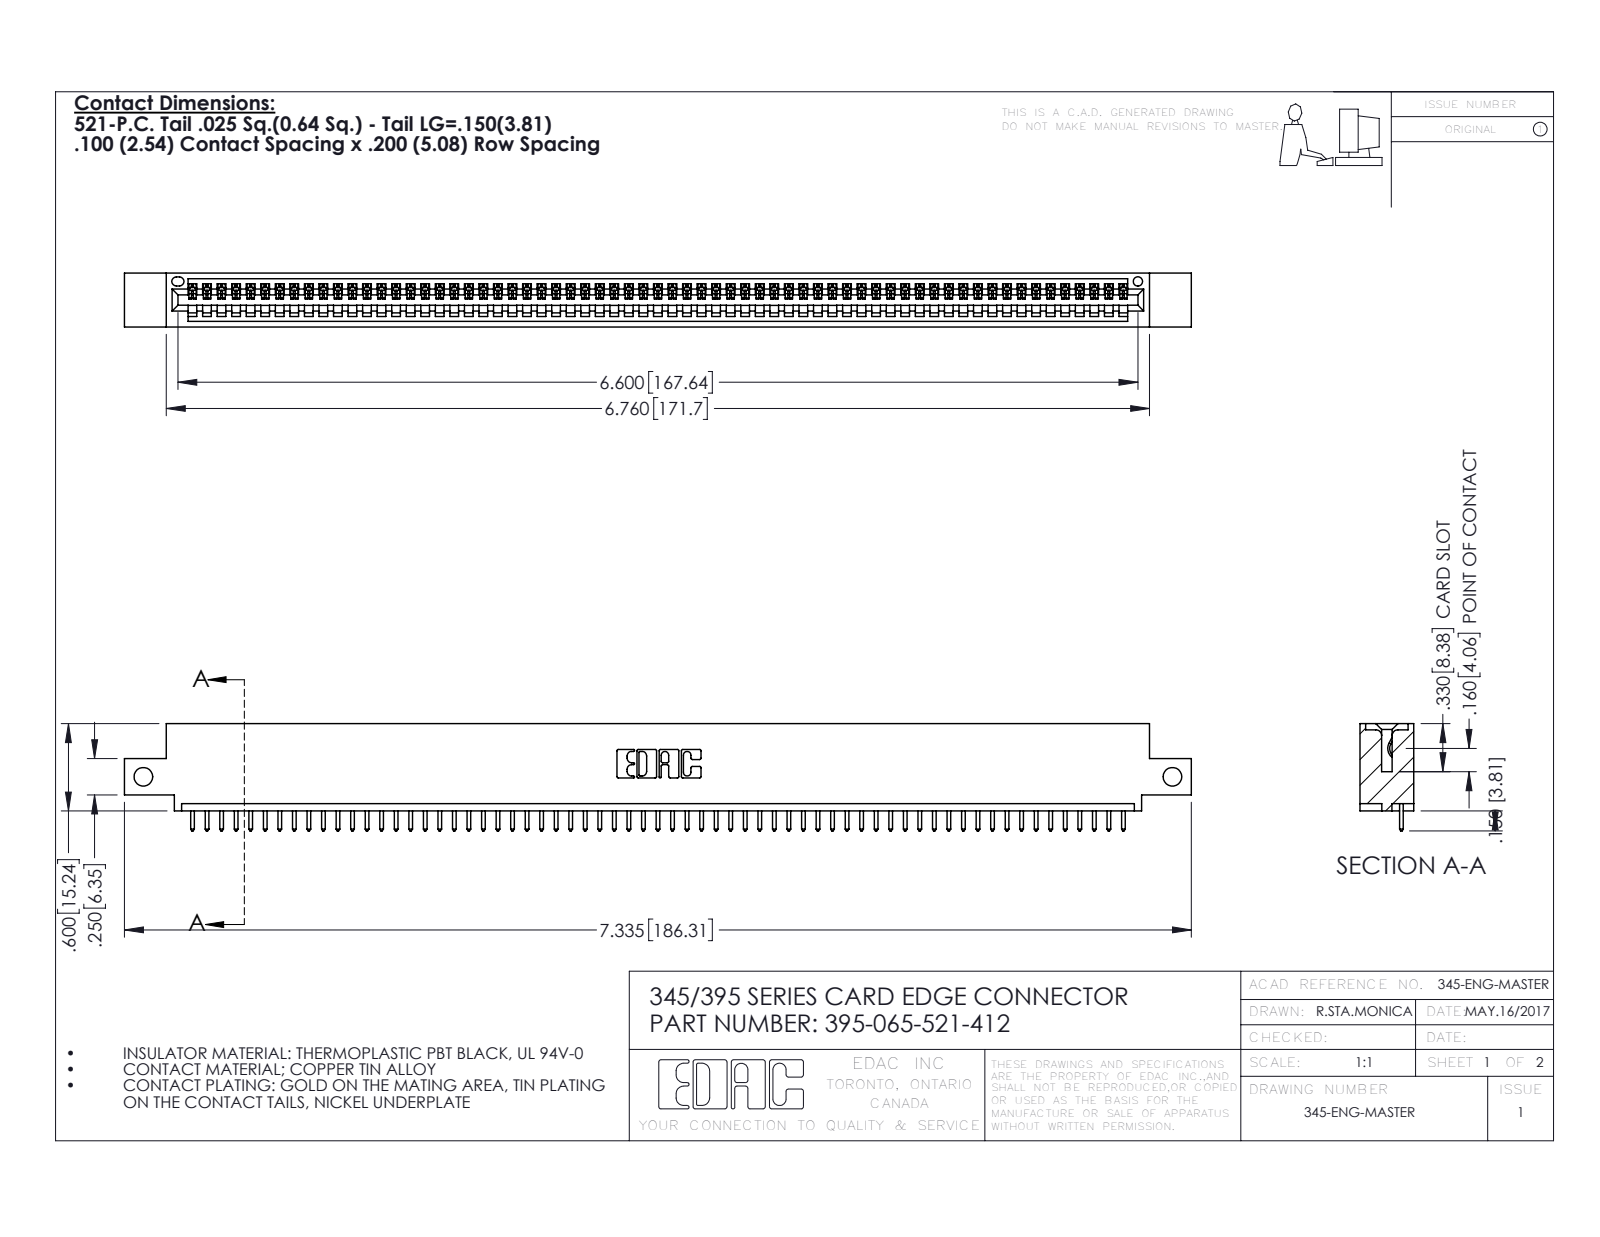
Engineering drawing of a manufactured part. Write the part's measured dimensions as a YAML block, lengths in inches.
part_name: "395-065-521-412; 345 Part_0.110 Offset - Side Mount; 345-292-001_345-293-121"
step_written_by: "SolidWorks 2016 (CONFIG_CONTROL_DESIGN)"
units: inches
bodies: {solids: 66, faces: 3900, planar: 2684, cylindrical: 1216, other: 0}
overall_size: [7.335, 0.737, 0.37]
volume: 1.07
surface_area: 35.4
round_holes:
  - {diameter: 0.128, count: 2}
  - {diameter: 0.064, count: 1}
partial_cylinders:
  - {radius: 0.006, count: 130}
  - {radius: 0.01, count: 130}
  - {radius: 0.01, count: 22}
  - {radius: 0.007, count: 6}
  - {radius: 0.031, count: 6}
  - {radius: 0.026, count: 3}
  - {radius: 0.031, count: 2}
  - {radius: 0.04, count: 2}
face_to_face_distances: [0.298, 0.072, 0.37, 0.2, 0.098, 0.272, 0.025, 0.225, 0.149, 0.072]
hole_center_spacings: [7.075]
